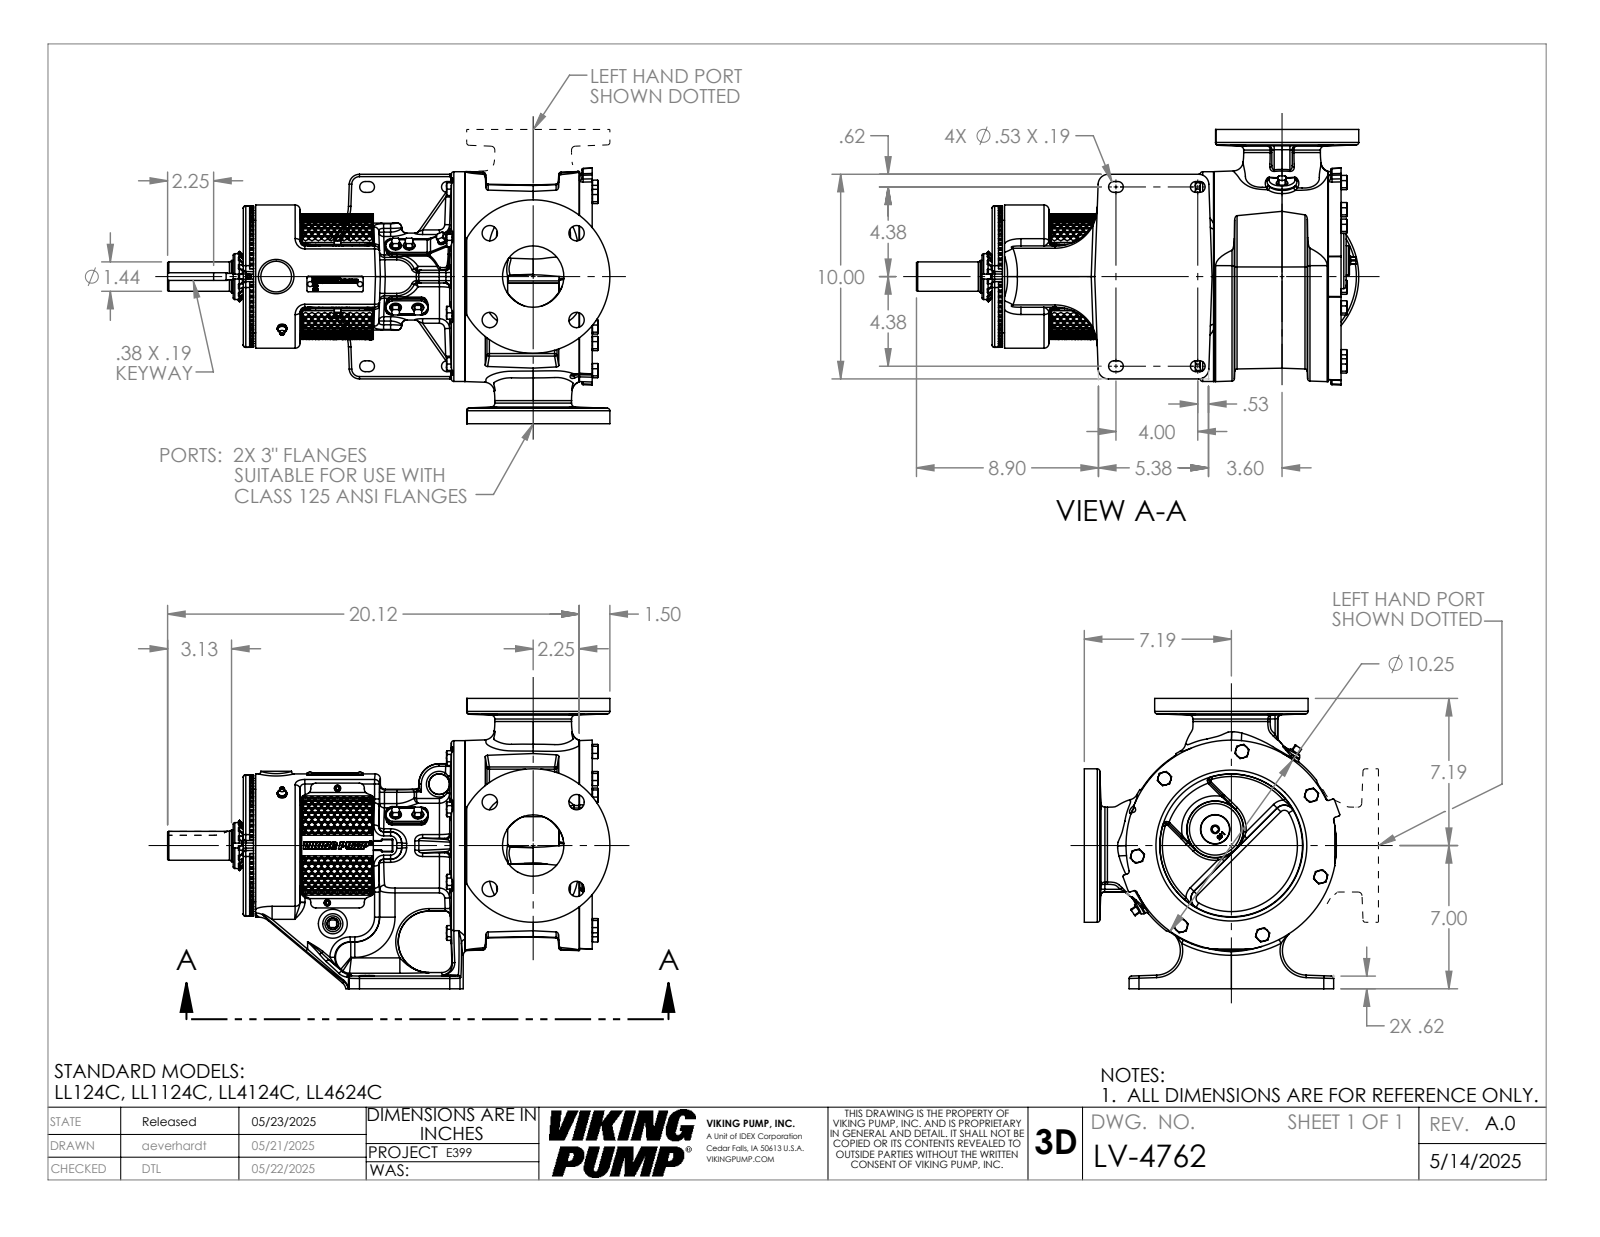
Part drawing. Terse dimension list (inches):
name: LV-4762
written by: SolidWorks 2024 (AUTOMOTIVE_DESIGN)
unit: in
bodies: 1 solid, 4103 faces (1339 planar, 851 cylindrical, 1913 other)
size: 21.622 × 14.19 × 12.492
volume: 874.9 in³; area: 1 325 in²
holes: 8× ⌀0.75, 8× ⌀1.094, 6× ⌀0.199, 6× ⌀0.25, 3× ⌀0.159, 2× ⌀0.266, 2× ⌀0.313, 1× ⌀1.577, 1× ⌀1.593, 1× ⌀1.83, 1× ⌀2.44, 1× ⌀5.25
bosses: 10× ⌀0.625, 5× ⌀0.625, 3× ⌀0.437, 3× ⌀0.312, 2× ⌀7.5, 2× ⌀3.75, 1× ⌀10.25, 1× ⌀7
rounds: 109× R0.063, 103× R0.12, 74× R0.069, 48× R0.24, 18× R0.03, 14× R0.25, 14× R0.75, 12× R0.06
face distances: 14.19, 1, 14.307, 3.537, 10.77, 0.5, 2.25, 2.143, 5.68, 16.45
hole spacings: 3, 4.243, 1.375, 2.18, 3.609, 4.446, 4.625, 6.404
